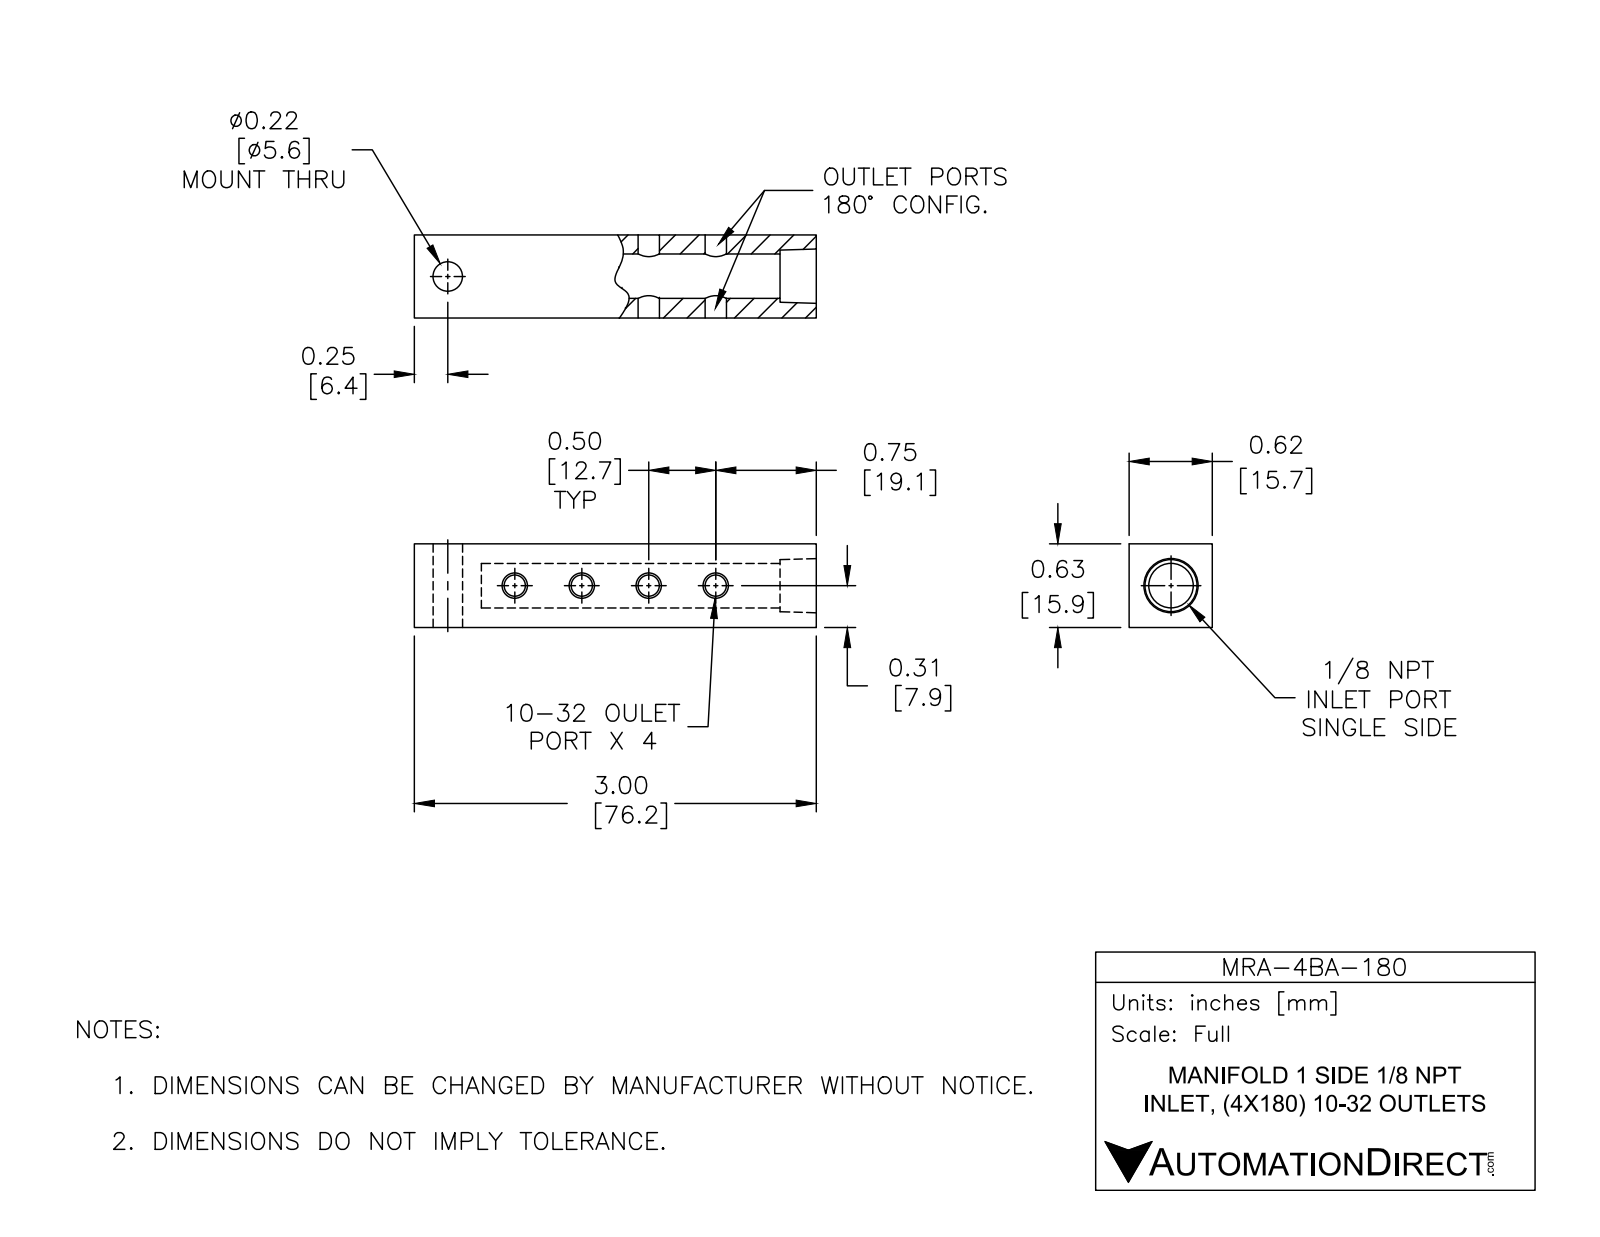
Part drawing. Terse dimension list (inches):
name: MRA-4BA-180
written by: SolidWorks 2015 (CONFIG_CONTROL_DESIGN)
unit: in
bodies: 1 solid, 30 faces (8 planar, 20 cylindrical, 2 other)
size: 3 × 0.625 × 0.62
volume: 0.889 in³; area: 11.55 in²
holes: 4× ⌀0.159, 1× ⌀0.22, 1× ⌀0.332
face distances: 0.625, 0.62, 3, 0.5, 2.5, 2.73, 2.23, 0.27
hole spacings: 0.5, 1, 1.5
